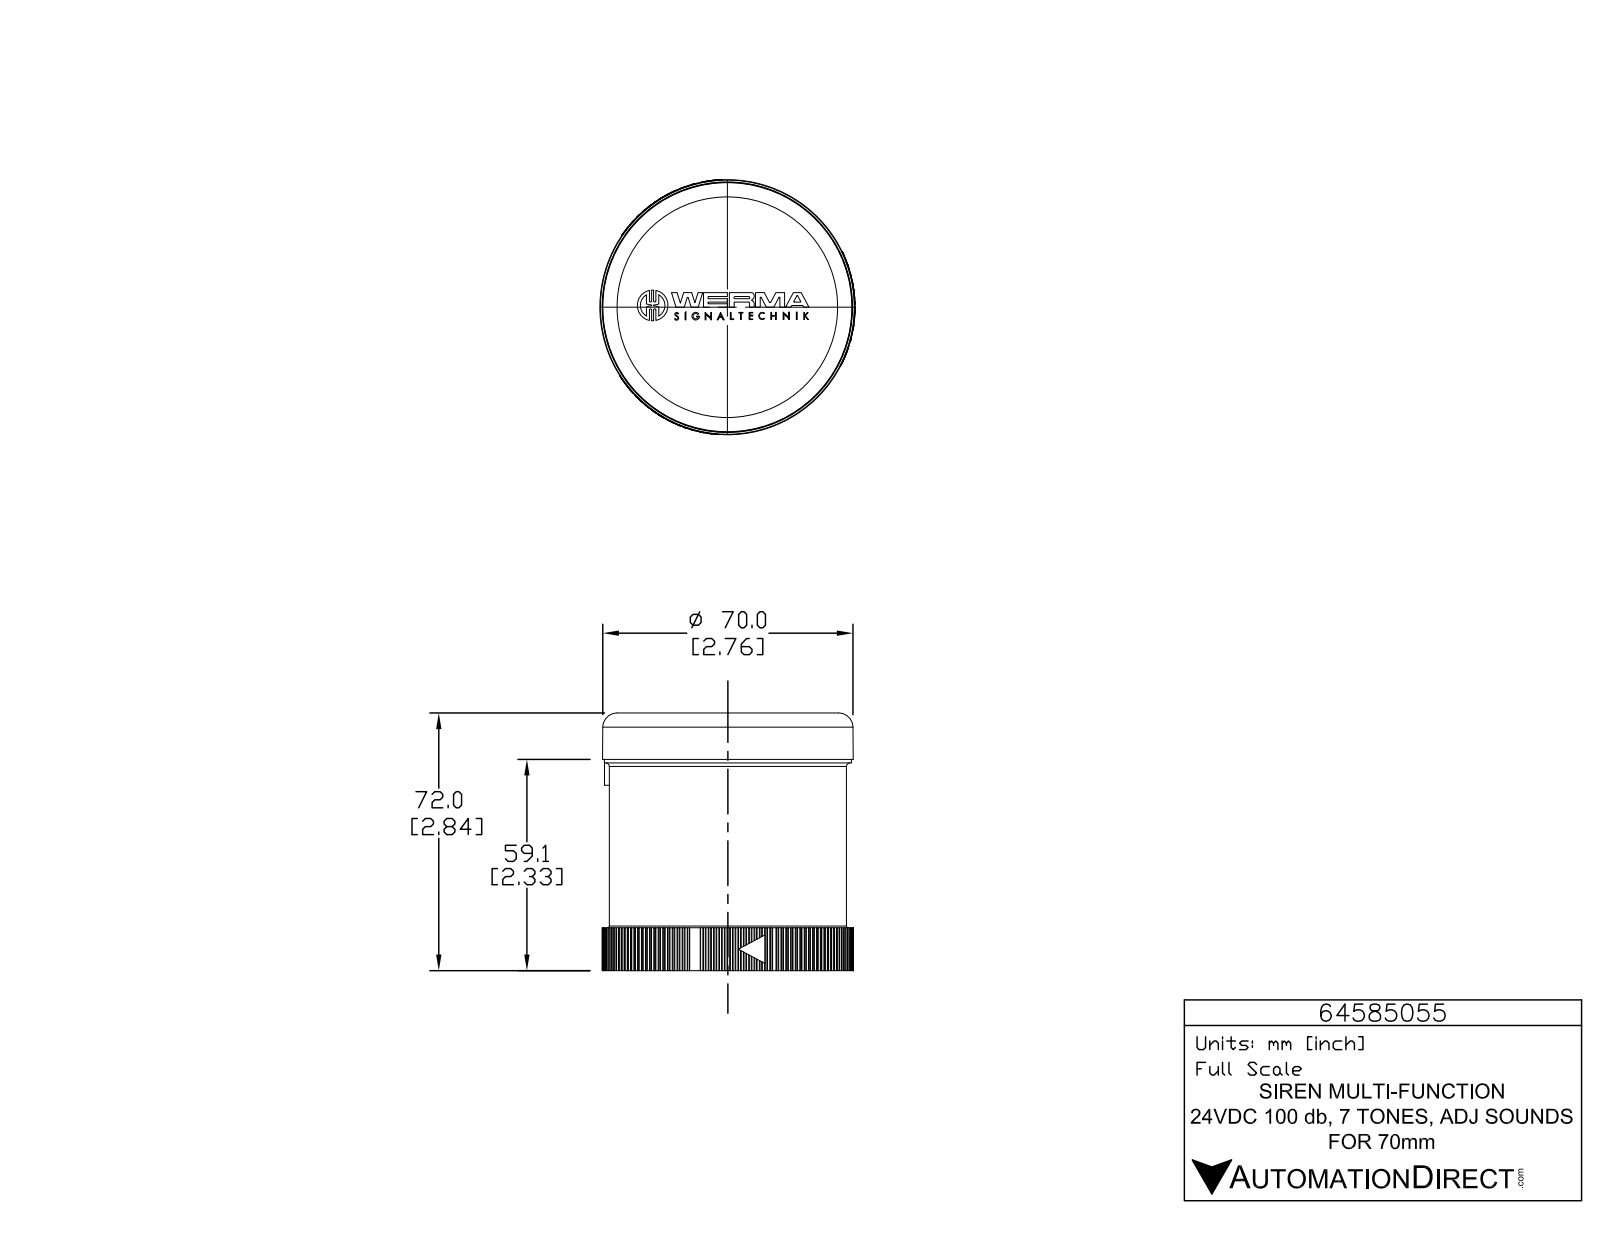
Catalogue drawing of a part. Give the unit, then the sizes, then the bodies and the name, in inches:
Units: inches
Overall size (bounding box): 2.835 × 2.762 × 2.762
Round holes (diameter × count): ⌀0.039 ×3, ⌀0.068 ×1, ⌀0.099 ×1, ⌀0.395 ×1, ⌀2.575 ×1, ⌀2.61 ×1, ⌀2.661 ×1
Round bosses / shafts (diameter × count): ⌀0.226 ×3, ⌀0.056 ×3, ⌀2.756 ×1, ⌀2.717 ×1, ⌀2.606 ×1, ⌀2.559 ×1, ⌀0.395 ×1, ⌀0.099 ×1
Partial cylindrical surfaces — rounded edges, fillets, slot ends (radius × count): R0.008 ×285, R0.006 ×6, R0.008 ×6, R0.008 ×6, R0.008 ×6, R0.131 ×6, R0.006 ×4, R0.014 ×4
Main face-to-face distances: 0.118, 0.079, 2.201, 2.378, 0.177, 2.26, 0.059, 0.039, 2.457, 0.256
Hole centre spacings: 0.378, 0.388, 0.536, 0.572, 0.849, 0.917
Volume: 13.2 in³ · Surface area: 68.48 in²
Bodies: 1 solid, 1915 faces (1231 planar, 671 cylindrical, 13 other)
Part name (STEP PRODUCT): 64585055
STEP written by: SolidWorks 2021 (CONFIG_CONTROL_DESIGN)
